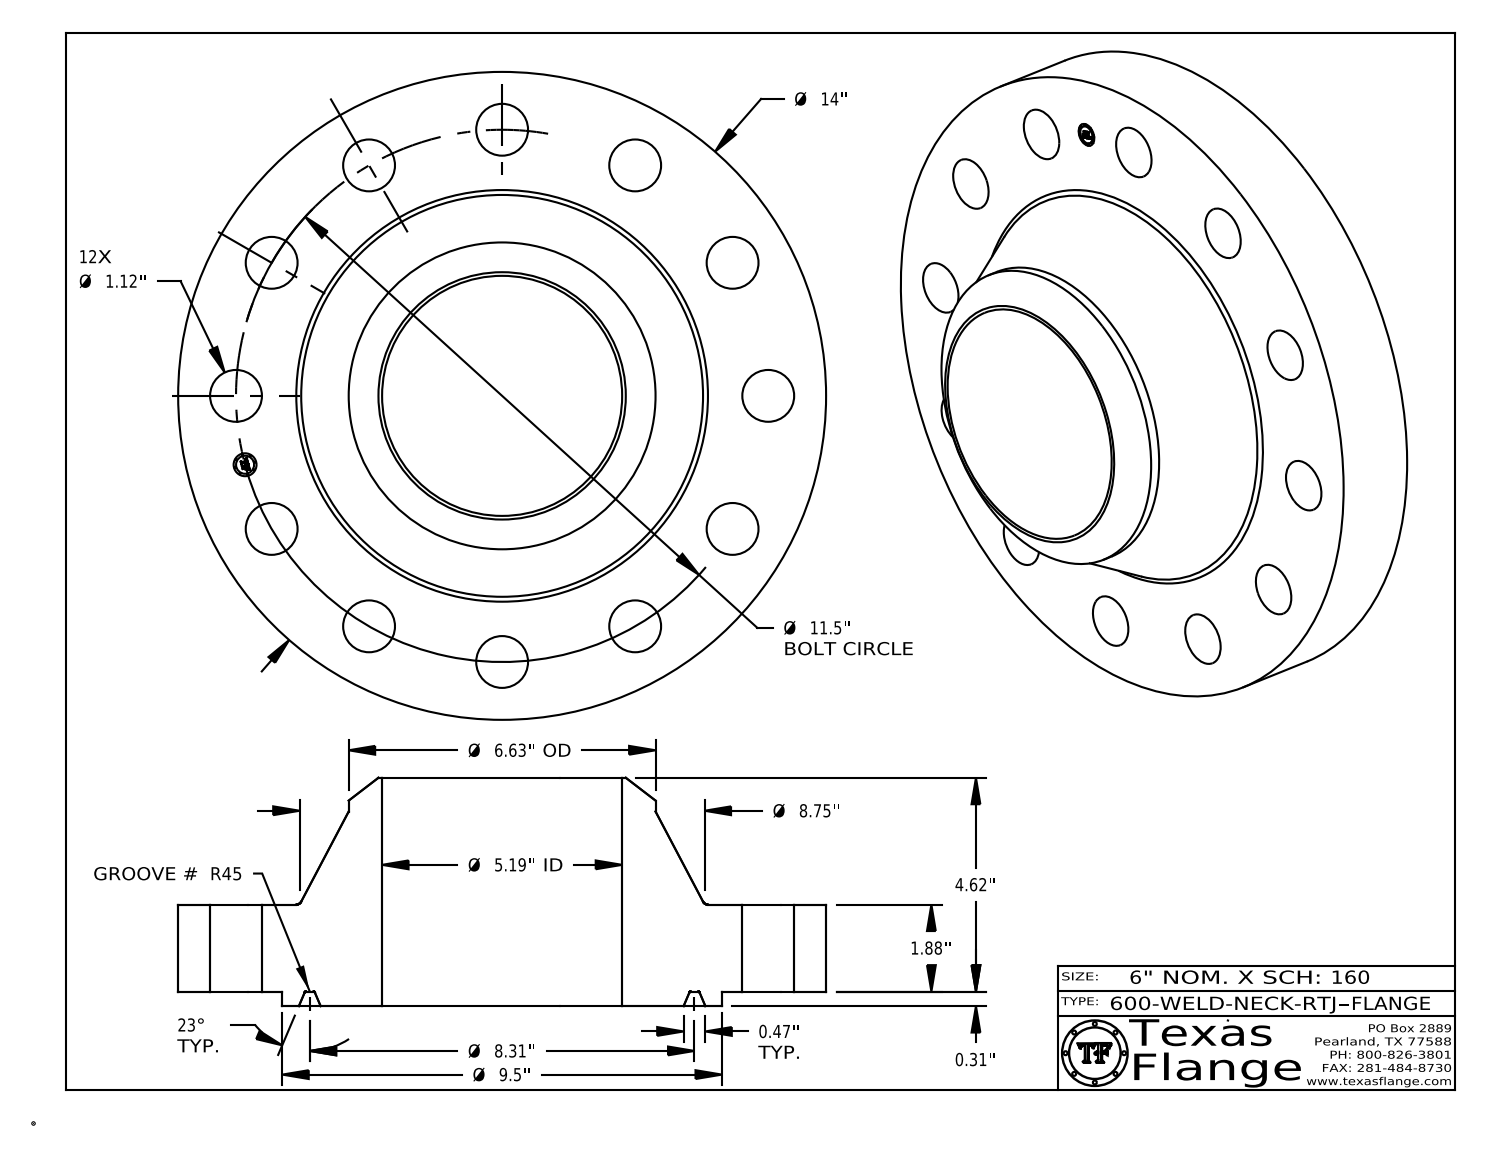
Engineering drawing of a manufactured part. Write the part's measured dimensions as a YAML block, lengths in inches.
part_name: "600-WELD-NECK-RTJ"
step_written_by: "CATIA V5 STEP AP214 (AUTOMOTIVE_DESIGN)"
units: inches
bodies: {solids: 1, faces: 437, planar: 371, cylindrical: 52, other: 14}
overall_size: [14, 14, 4.933]
volume: 298.5
surface_area: 541.4
round_holes:
  - {diameter: 1.12, count: 12}
  - {diameter: 0.495, count: 1}
  - {diameter: 5.187, count: 1}
round_bosses_or_shafts:
  - {diameter: 0.03, count: 8}
  - {diameter: 14, count: 1}
  - {diameter: 9.5, count: 1}
  - {diameter: 6.63, count: 1}
  - {diameter: 0.39, count: 1}
face_to_face_distances: [1.88, 0.313, 2.193, 4.933, 4.62, 2.74, 2.178, 1.865, 0.015, 2.755]
hole_center_spacings: [5.75, 8.132, 11.108, 2.977, 5.75, 9.959, 11.5, 2.976]
